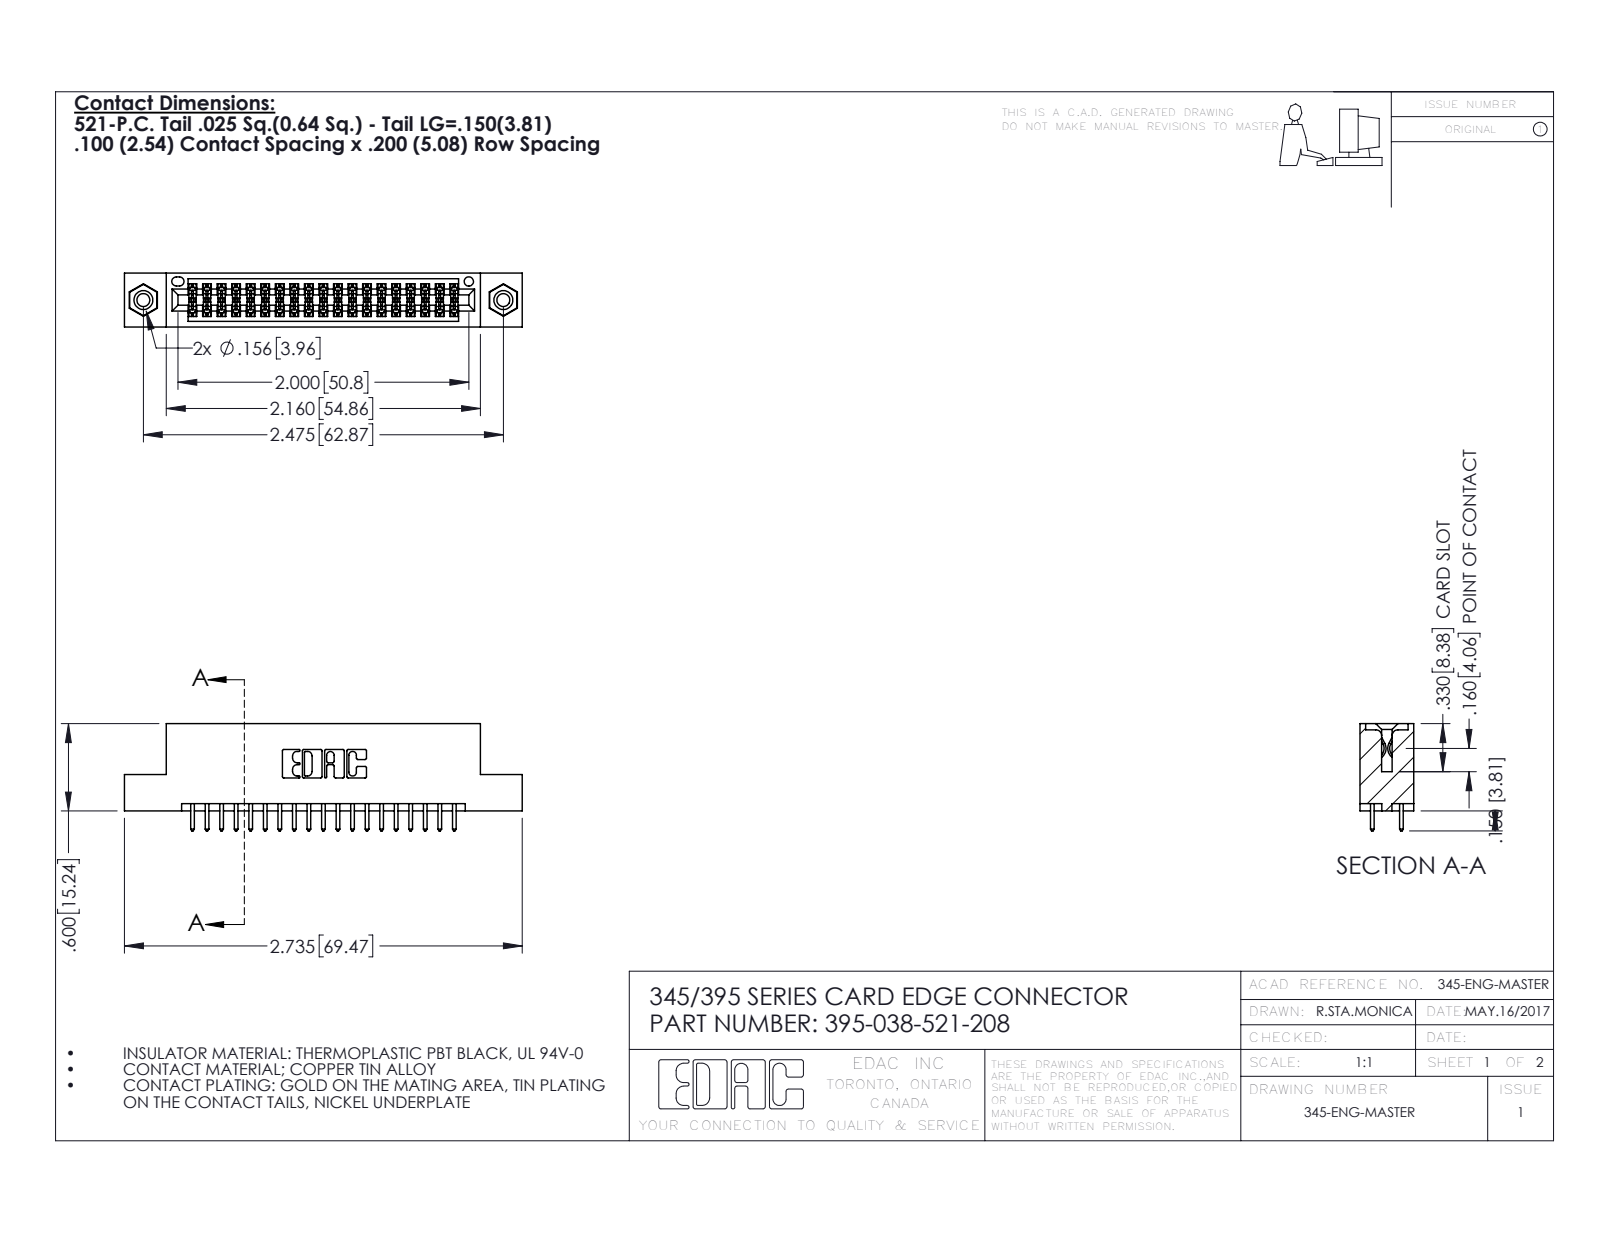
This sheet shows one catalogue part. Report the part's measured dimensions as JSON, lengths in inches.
{"part_name": "345-292-001_345-293-121; 345 Part_Flush Mounting Lugs - 0.156 Dia-TI; 395-038-521-208; 345-250-001_345-250-003-102", "step_written_by": "SolidWorks 2016 (CONFIG_CONTROL_DESIGN)", "units": "inches", "bodies": {"solids": 41, "faces": 2086, "planar": 1366, "cylindrical": 704, "other": 16}, "overall_size": [2.735, 0.737, 0.37], "volume_in3": 0.397, "surface_area_in2": 14.1, "round_holes": [[0.089, 2], [0.125, 2], [0.156, 2], [0.064, 1]], "round_bosses_or_shafts": [[0.155, 2]], "partial_cylinders_radius": [[0.006, 57], [0.01, 38], [0.01, 22], [0.007, 6], [0.031, 6], [0.026, 3], [0.014, 2], [0.019, 2]], "face_to_face_distances": [0.072, 0.298, 0.2, 0.37, 0.098, 0.272, 0.025, 0.225, 0.175, 0.6], "hole_center_spacings": [0.27, 2.241, 2.475]}
